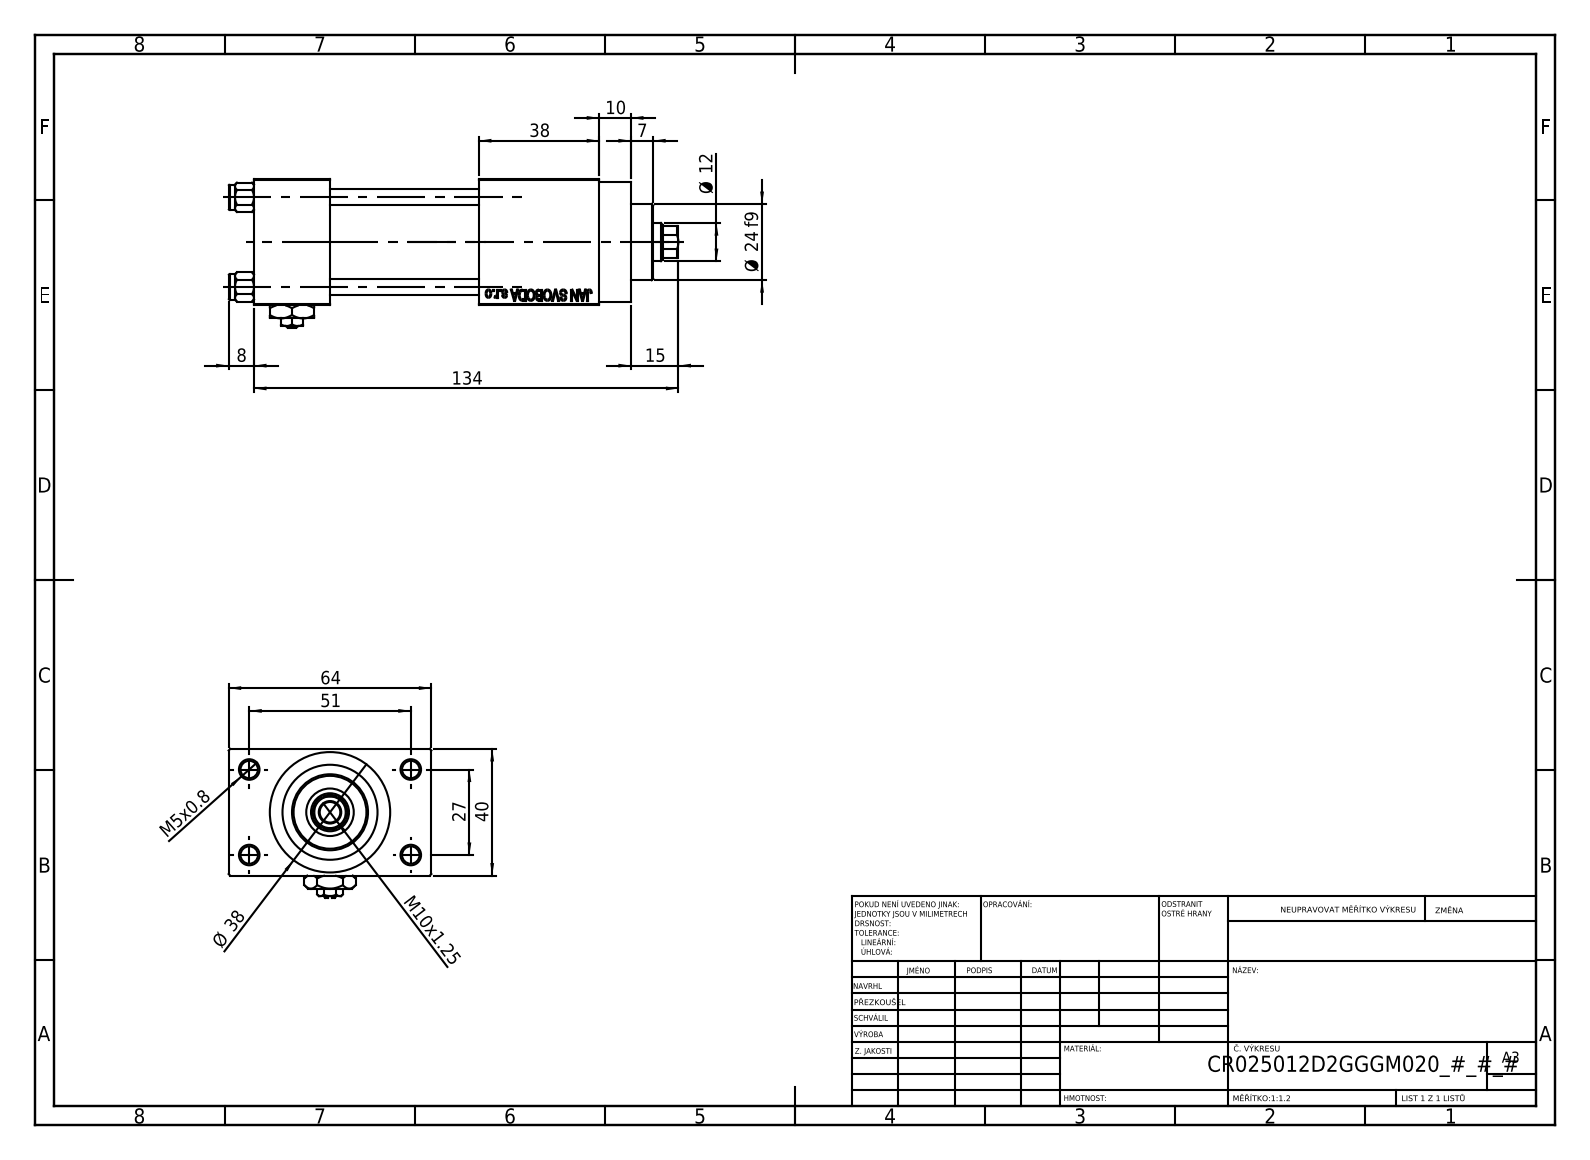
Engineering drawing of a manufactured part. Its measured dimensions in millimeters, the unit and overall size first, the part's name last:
Units: millimetres
Overall size (bounding box): 142 × 64 × 47
Round holes (diameter × count): ⌀5 ×4, ⌀5.5 ×4, ⌀20 ×3, ⌀7 ×2, ⌀13.16 ×2, ⌀6.5 ×1, ⌀12 ×1, ⌀15 ×1, ⌀25 ×1, ⌀30 ×1
Round bosses / shafts (diameter × count): ⌀8 ×4, ⌀38 ×1, ⌀31 ×1, ⌀24 ×1
Partial cylindrical surfaces — rounded edges, fillets, slot ends (radius × count): R5.5 ×1
Main face-to-face distances: 40, 52, 12, 47, 24, 71, 64, 38, 109, 85
Hole centre spacings: 11.37, 20.01, 28.3, 28.85, 29.89, 39.66, 48.34, 27
Volume: 174 160 mm³ · Surface area: 62 753 mm²
Bodies: 12 solids, 1155 faces (519 planar, 96 cylindrical, 540 other)
Part name (STEP PRODUCT): V215CR_VCP_D; Zatka_pro_OIL_PORT; V215CR_D_TYCINKA; NUT_M5_D (+2 more)
STEP written by: SolidWorks 2019 (CONFIG_CONTROL_DESIGN)
